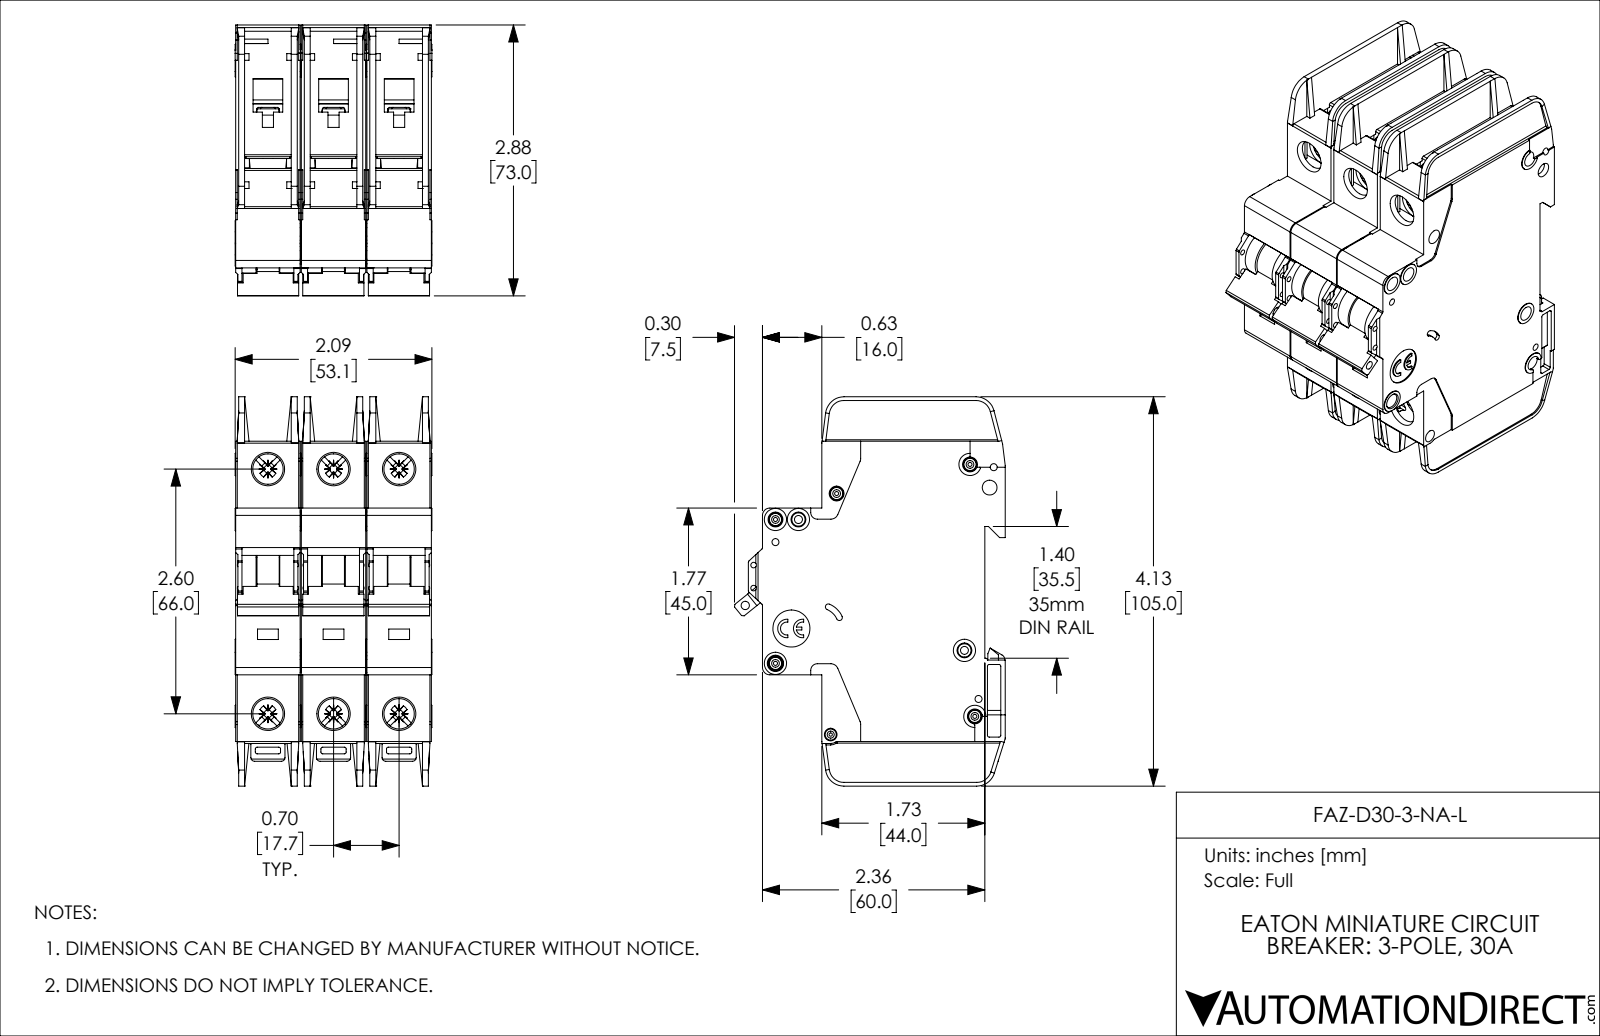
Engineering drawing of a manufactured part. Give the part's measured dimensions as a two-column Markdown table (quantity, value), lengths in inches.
| quantity | value |
| --- | --- |
| part name | FAZ-D30-3-NA-L |
| STEP written by | SolidWorks 2019 (AUTOMOTIVE_DESIGN) |
| units | inches |
| bodies | 3 solids, 3381 faces (2013 planar, 1071 cylindrical, 297 other) |
| overall size | 4.134 × 2.876 × 2.091 |
| volume | 14.05 in³ |
| surface area | 123 in² |
| round holes (diameter × count) | 0.157 × 8, 0.323 × 6, 0.043 × 5, 0.075 × 4, 0.059 × 2, 0.085 × 2, 0.035 × 1, 0.089 × 1, 0.098 × 1, 0.134 × 1, 0.394 × 1 |
| round bosses / shafts (diameter × count) | 0.13 × 5, 0.236 × 4, 0.118 × 4, 0.098 × 3 |
| partial cylindrical surfaces (radius × count) | 0.02 × 72, 0.016 × 30, 0.039 × 18, 0.043 × 12, 0.079 × 12, 0.008 × 6, 0.01 × 6, 0.028 × 6 |
| main face-to-face distances | 0.697, 0.047, 1.394, 0.685, 0.591, 1.382, 0.744, 0.65, 0.106, 0.094 |
| hole center spacings | 0.697, 2.69, 2.598, 0.244, 0.537, 0.87, 1.394, 2.948 |
